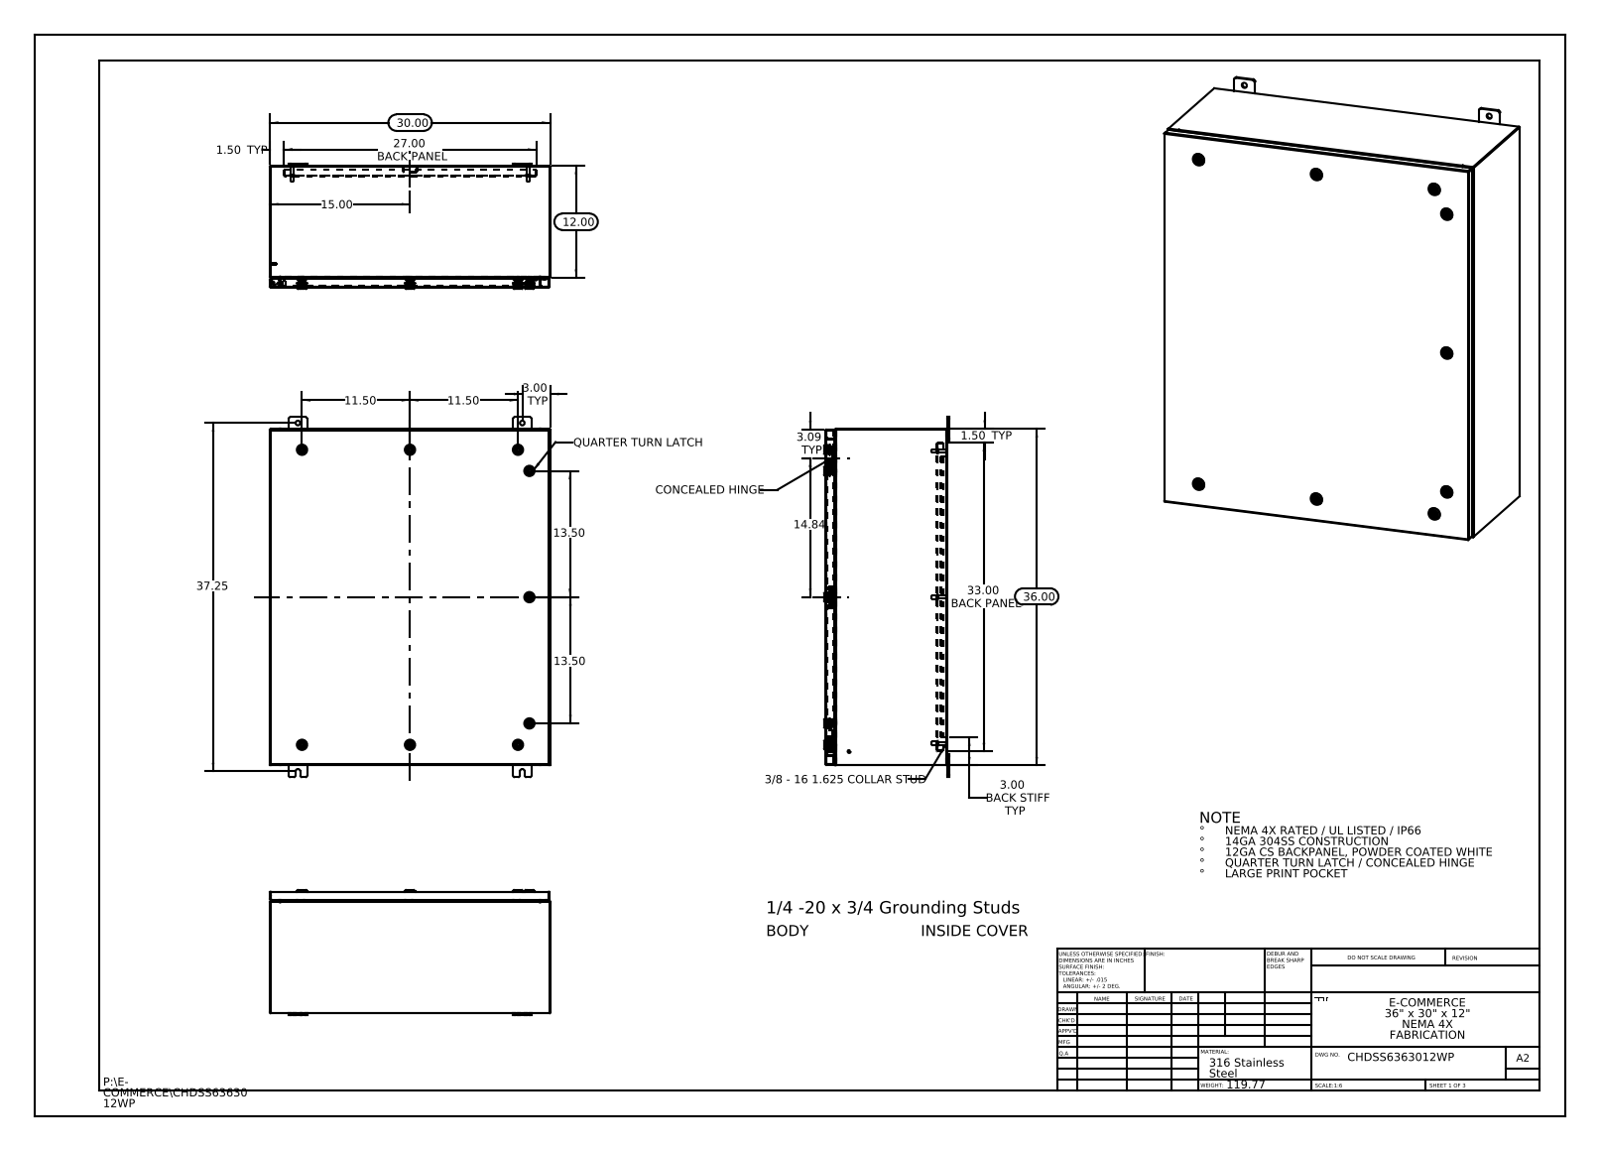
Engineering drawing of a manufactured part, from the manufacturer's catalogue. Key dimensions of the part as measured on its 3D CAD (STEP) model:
Part name (STEP PRODUCT): CHDSS6363012WP Bottom; Washer-221320-IB-Industrilas_Washer-221320-IB-Industrilas; CHDSS6363012WP Mounting Feet; CHDSS6363012WP Body (+8 more)
STEP written by: SolidWorks 2013 (CONFIG_CONTROL_DESIGN)
Units: inches
Bodies: 78 solids, 8020 faces (2324 planar, 2502 cylindrical, 3194 other)
Overall size (bounding box): 38.5 × 30 × 13.356
Volume: 424.6 in³ · Surface area: 10 582 in²
Round holes (diameter × count): ⌀0.5 ×10, ⌀0.197 ×9, ⌀0.394 ×9, ⌀0.4 ×9, ⌀0.63 ×9, ⌀0.787 ×9, ⌀0.136 ×6, ⌀0.211 ×1
Round bosses / shafts (diameter × count): ⌀0.236 ×11, ⌀1.102 ×9, ⌀0.78 ×9, ⌀0.626 ×9, ⌀0.61 ×9, ⌀0.531 ×9, ⌀0.392 ×9, ⌀0.114 ×9
Partial cylindrical surfaces — rounded edges, fillets, slot ends (radius × count): R0.006 ×297, R0.118 ×297, R0.028 ×108, R0.02 ×36, R0.197 ×36, R0.013 ×26, R0.19 ×24, R0.088 ×22
Main face-to-face distances: 0.075, 0.074, 13.01, 12.935, 12.936, 12.861, 0.104, 1, 1.075, 11.861
Hole centre spacings: 11.55, 15.625, 29.694, 33.598, 14.843, 25.25, 31.55, 0.688
